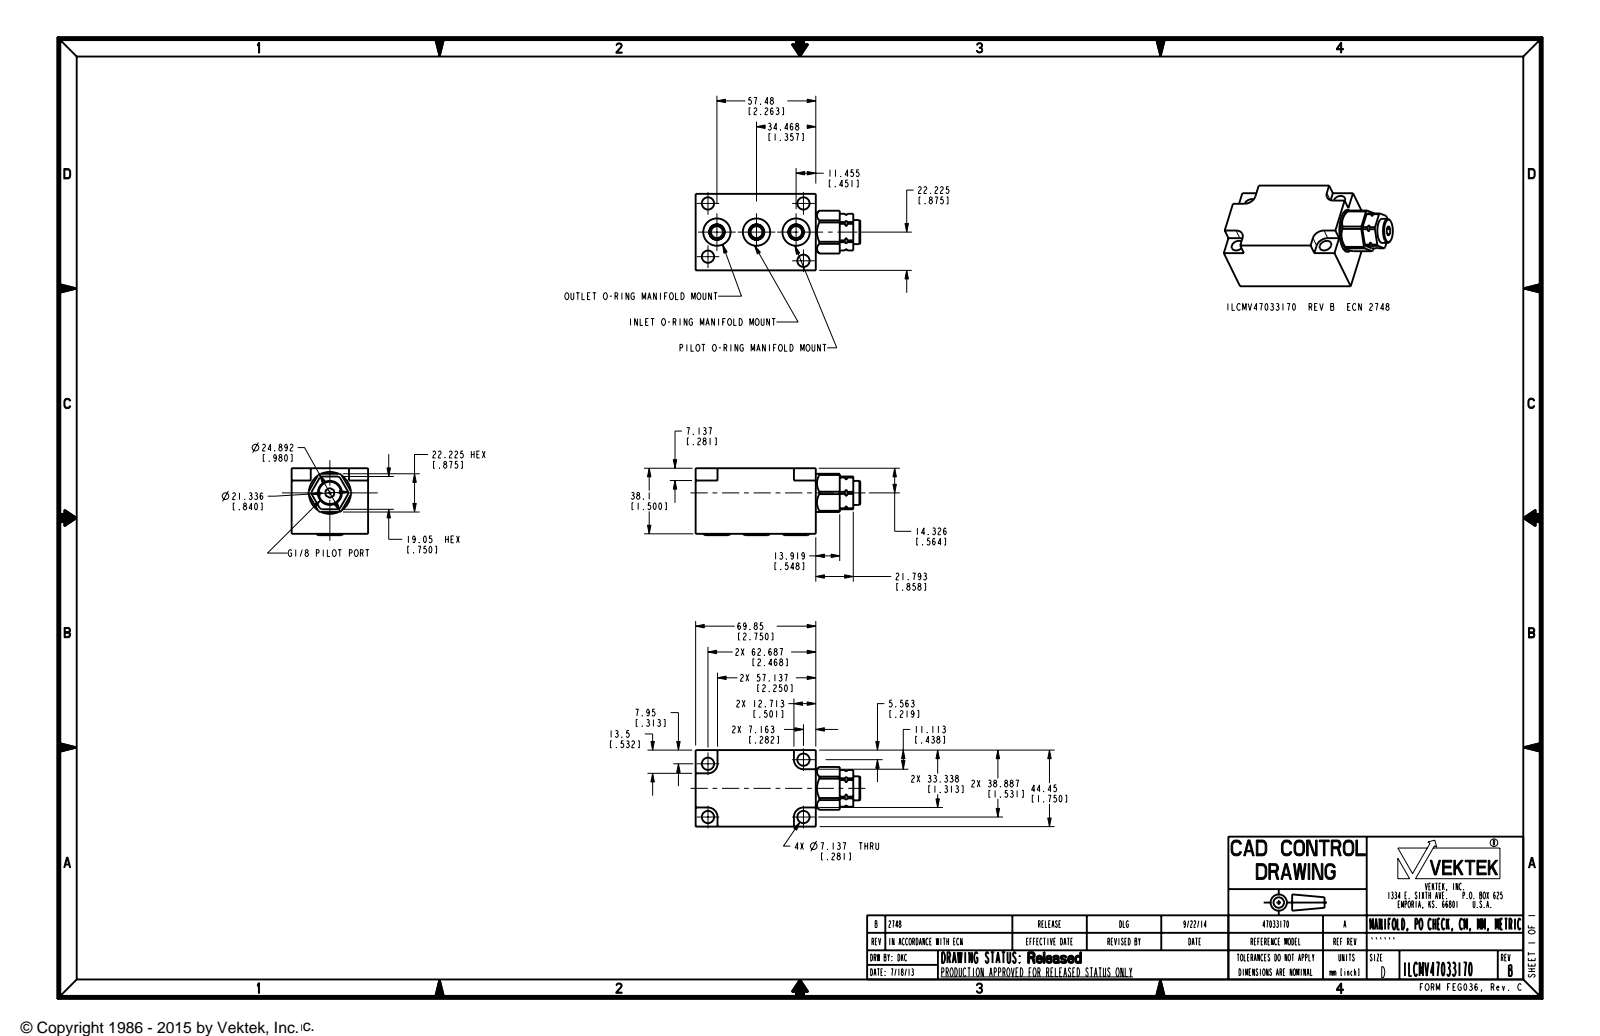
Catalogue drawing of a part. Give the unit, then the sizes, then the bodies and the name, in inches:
Units: inches
Overall size (bounding box): 3.768 × 1.75 × 1.531
Round holes (diameter × count): ⌀0.272 ×3, ⌀0.281 ×3, ⌀0.625 ×3, ⌀0.281 ×1, ⌀0.348 ×1
Round bosses / shafts (diameter × count): ⌀0.856 ×1, ⌀0.55 ×1
Partial cylindrical surfaces — rounded edges, fillets, slot ends (radius × count): R0.219 ×4, R0.42 ×1, R0.49 ×1
Main face-to-face distances: 1.75, 1.5, 2.75, 0.875, 1.219, 0.281, 0.105, 1.114, 1.395, 0.063
Hole centre spacings: 0.677, 1.259, 2.087, 0.598, 0.687, 0.906, 0.906, 1.218
Volume: 7.079 in³ · Surface area: 33 in²
Bodies: 1 solid, 138 faces (50 planar, 54 cylindrical, 34 other)
Part name (STEP PRODUCT): ILCMV47033170
STEP written by: PRO/ENGINEER BY PARAMETRIC TECHNOLOGY CORPORATION, 2013320 (CONFIG_CONTROL_DESIGN)
